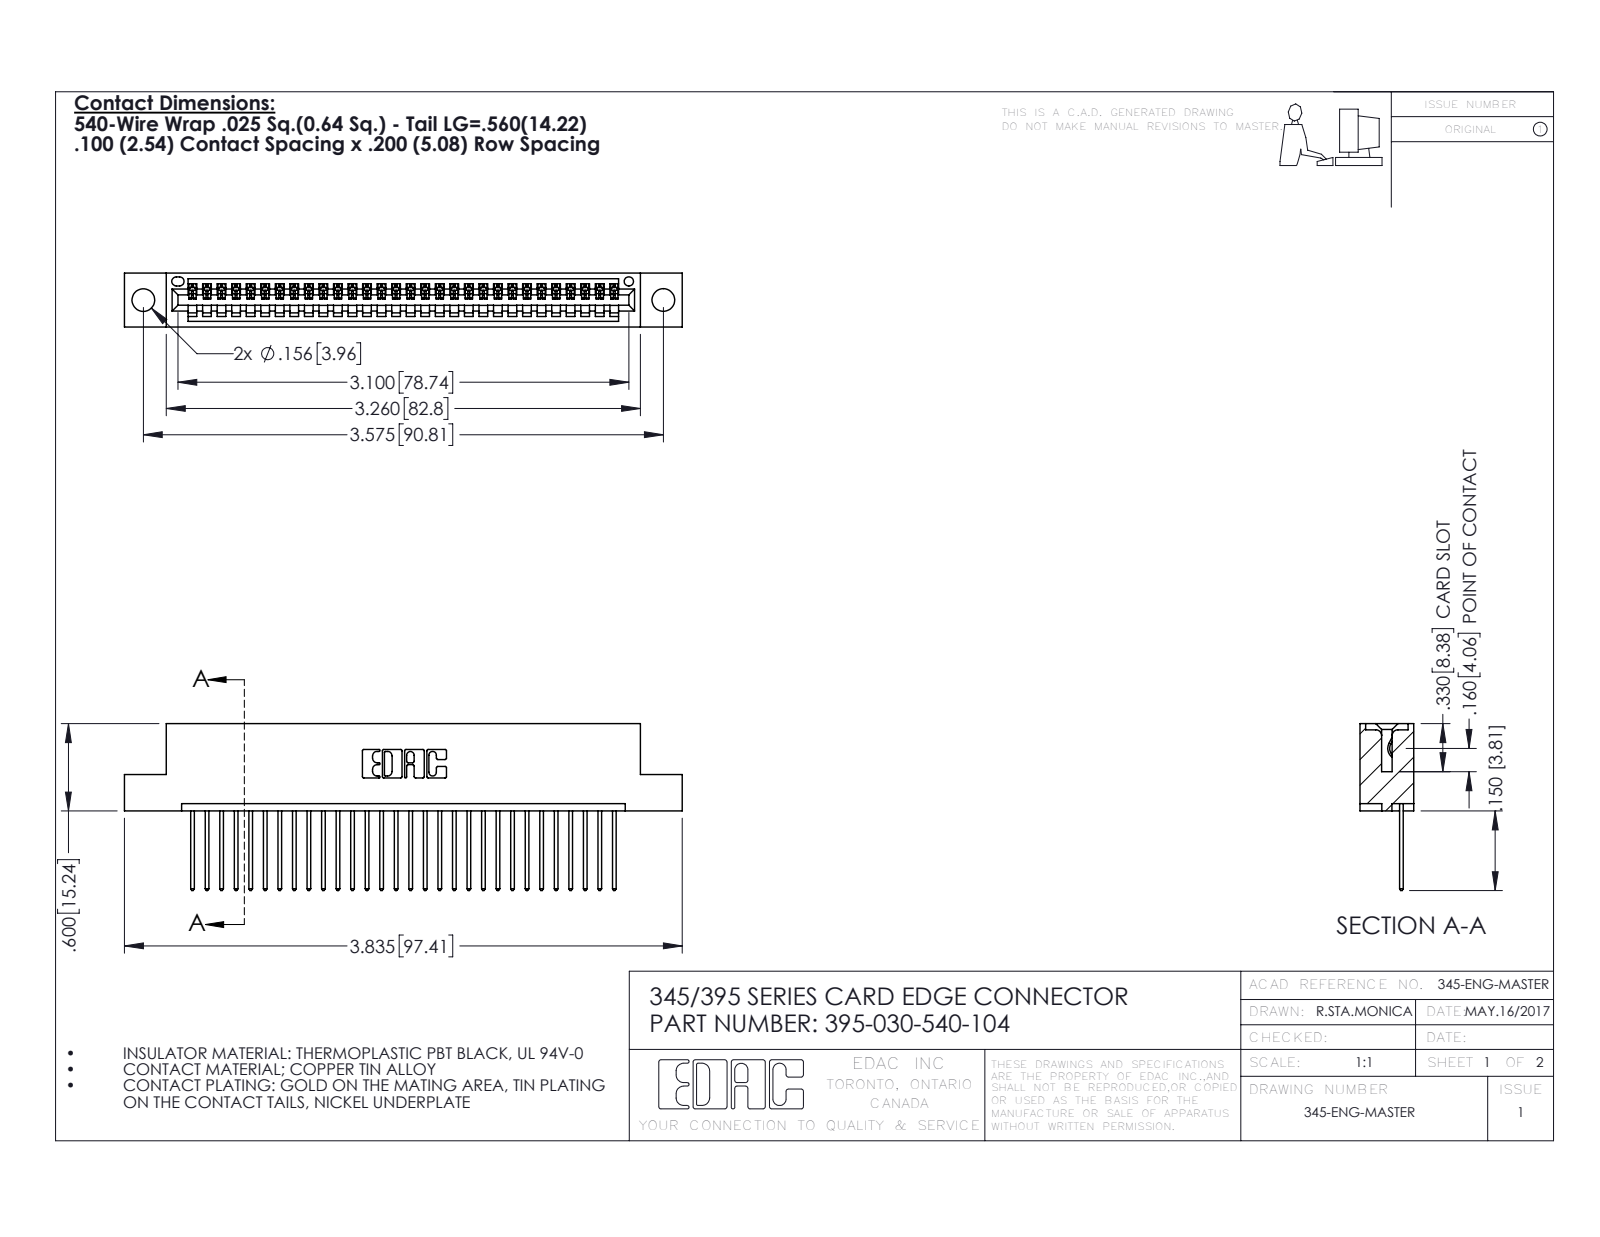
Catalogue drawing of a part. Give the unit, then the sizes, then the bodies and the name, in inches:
Units: inches
Overall size (bounding box): 3.835 × 1.147 × 0.37
Round holes (diameter × count): ⌀0.156 ×2, ⌀0.064 ×1
Partial cylindrical surfaces — rounded edges, fillets, slot ends (radius × count): R0.006 ×60, R0.01 ×60, R0.01 ×22, R0.007 ×6, R0.031 ×6, R0.026 ×3, R0.031 ×2, R0.04 ×2
Main face-to-face distances: 0.298, 0.072, 0.2, 0.37, 0.098, 0.272, 0.025, 0.225, 0.149, 0.072
Hole centre spacings: 0.27, 3.34, 3.575
Volume: 0.556 in³ · Surface area: 18.66 in²
Bodies: 31 solids, 1866 faces (1280 planar, 586 cylindrical, 0 other)
Part name (STEP PRODUCT): 395-030-540-104; 345-292-001_345-293-140; 345 Part_Flush Mounting Lugs - 0.156 Dia-TH
STEP written by: SolidWorks 2016 (CONFIG_CONTROL_DESIGN)
